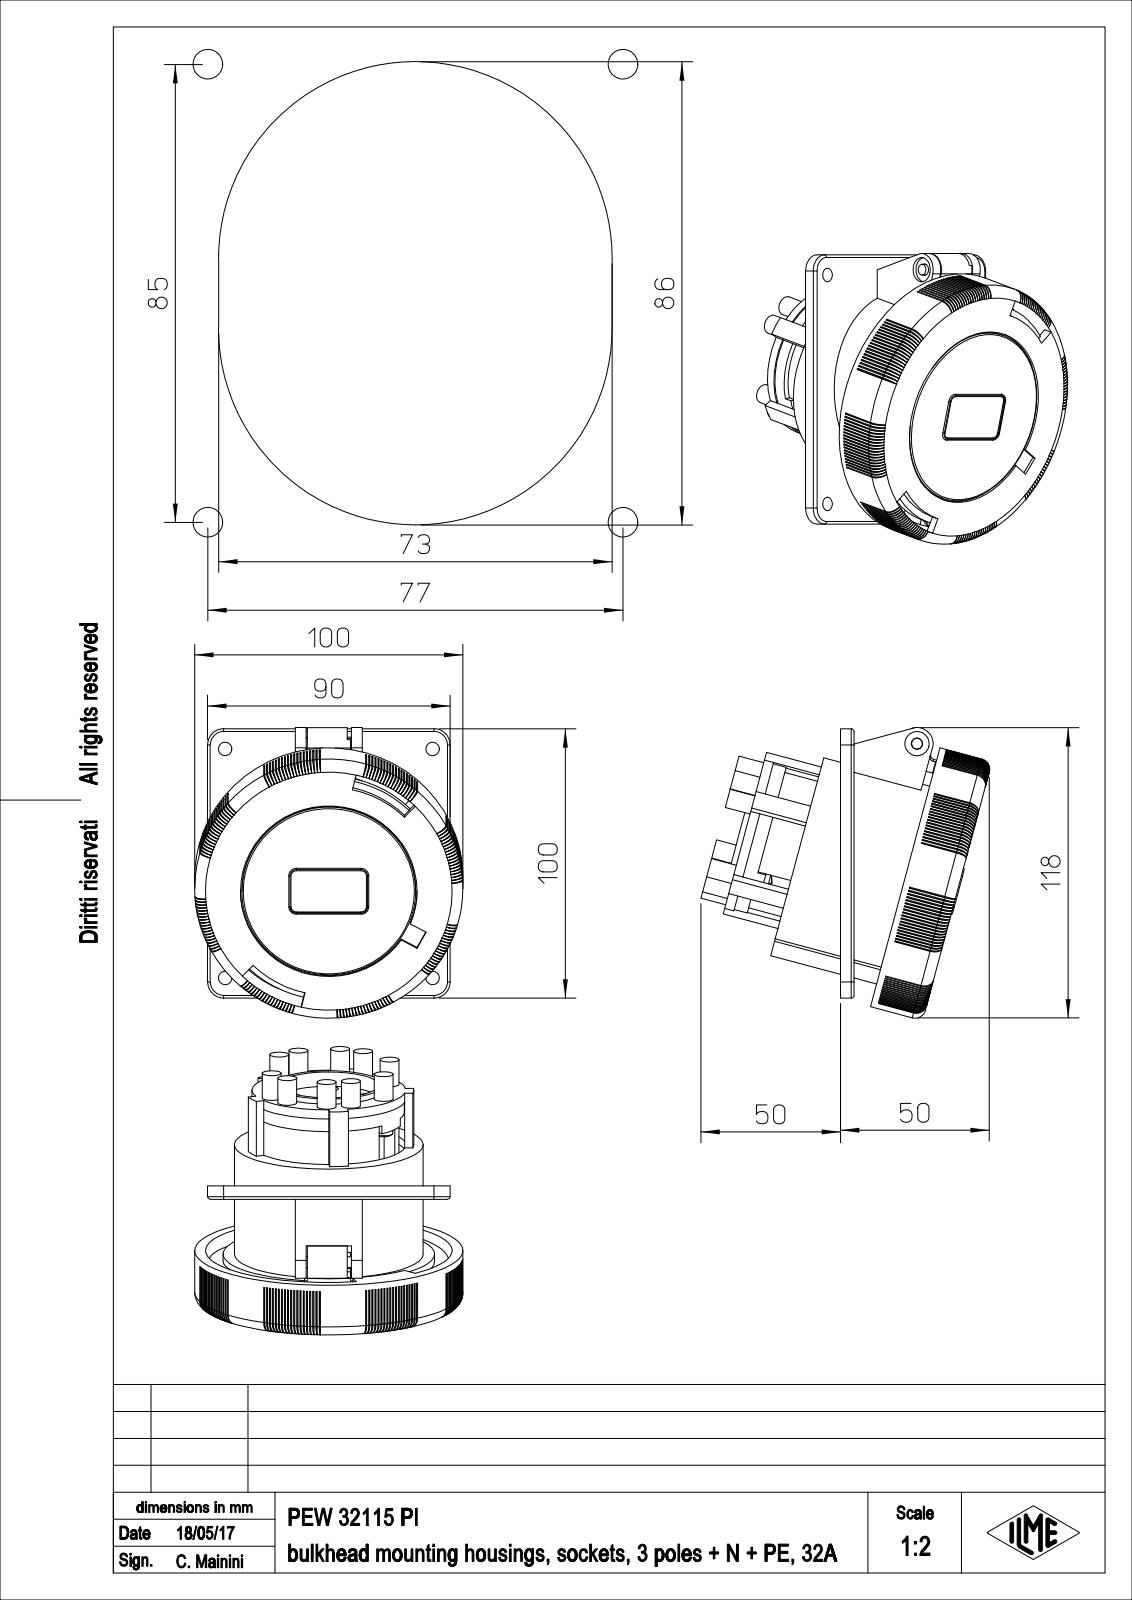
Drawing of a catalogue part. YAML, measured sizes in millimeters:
part_name: "PEW_32115_PI"
step_written_by: "PTC Creo Elements/Direct Modeling 19.0E 27-Jun-2016 (C) Parametric Technology GmbH (AUTOMOTIVE_DESIGN)"
units: millimeters
bodies: {solids: 1, faces: 1440, planar: 642, cylindrical: 307, other: 491}
overall_size: [107.91, 107.09, 99.5]
volume: 269783
surface_area: 105069
round_holes:
  - {diameter: 7, count: 5}
  - {diameter: 5, count: 4}
  - {diameter: 7.5, count: 4}
  - {diameter: 14, count: 4}
  - {diameter: 4.2, count: 1}
  - {diameter: 9, count: 1}
  - {diameter: 9.5, count: 1}
  - {diameter: 37, count: 1}
  - {diameter: 57, count: 1}
  - {diameter: 58.5, count: 1}
  - {diameter: 61.7, count: 1}
  - {diameter: 65.3, count: 1}
round_bosses_or_shafts:
  - {diameter: 7, count: 11}
  - {diameter: 6.7, count: 2}
  - {diameter: 99.5, count: 1}
  - {diameter: 85, count: 1}
  - {diameter: 78.5, count: 1}
  - {diameter: 75.5, count: 1}
  - {diameter: 70, count: 1}
  - {diameter: 64.5, count: 1}
partial_cylinders:
  - {radius: 3.6, count: 152}
  - {radius: 6, count: 6}
  - {radius: 0.4, count: 4}
  - {radius: 1, count: 4}
  - {radius: 2, count: 4}
  - {radius: 0.2, count: 3}
  - {radius: 4, count: 2}
  - {radius: 26, count: 2}
face_to_face_distances: [5, 3, 57.7, 2, 20, 17, 60.7, 40.7, 6.7, 11.19]
hole_center_spacings: [28.81, 17.81, 15.15, 15.14, 15.16, 28.82, 17.8, 15.12]
